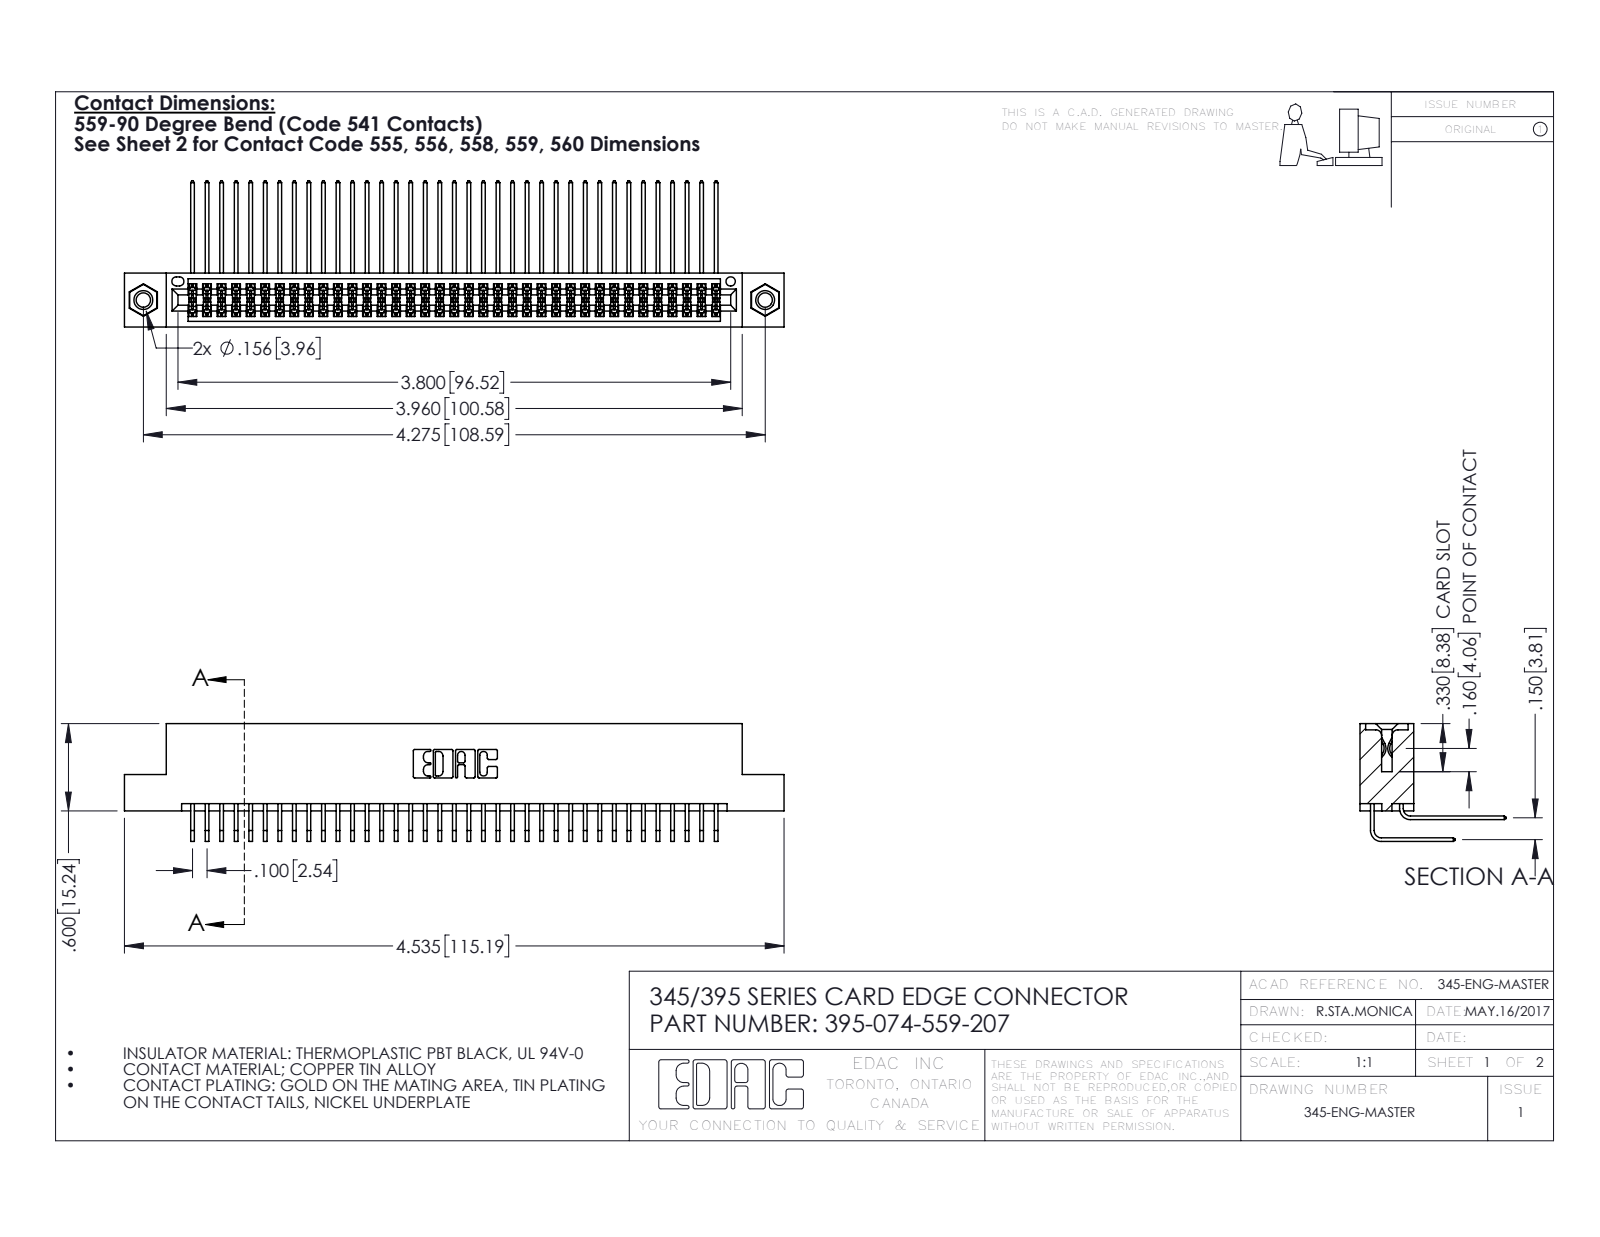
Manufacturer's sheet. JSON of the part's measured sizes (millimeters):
{"part_name": "345-292-001_559 Tail - 2; 345 Part_Flush Mounting Lugs - 0.156 Dia-TI; 345-292-001_558 559 Tail - 1; 395-074-559-207 (+1 more)", "step_written_by": "SolidWorks 2016 (CONFIG_CONTROL_DESIGN)", "units": "millimeters", "bodies": {"solids": 77, "faces": 4034, "planar": 2702, "cylindrical": 1316, "other": 16}, "overall_size": [115.2, 25.5, 20.5], "volume_mm3": 11600, "surface_area_mm2": 19020, "round_holes": [[2.5, 2], [3.2, 2], [4, 2], [1.6, 1]], "round_bosses_or_shafts": [[3.9, 2]], "partial_cylinders_radius": [[0.2, 112], [0.3, 22], [0.2, 6], [0.8, 6], [0.7, 3], [0.4, 2], [0.5, 2], [0.6, 2]], "face_to_face_distances": [1.8, 7.6, 5.1, 9.4, 2.5, 6.9, 0.6, 5.7, 4.4, 3.8], "hole_center_spacings": [6.9, 102.6, 108.6]}
